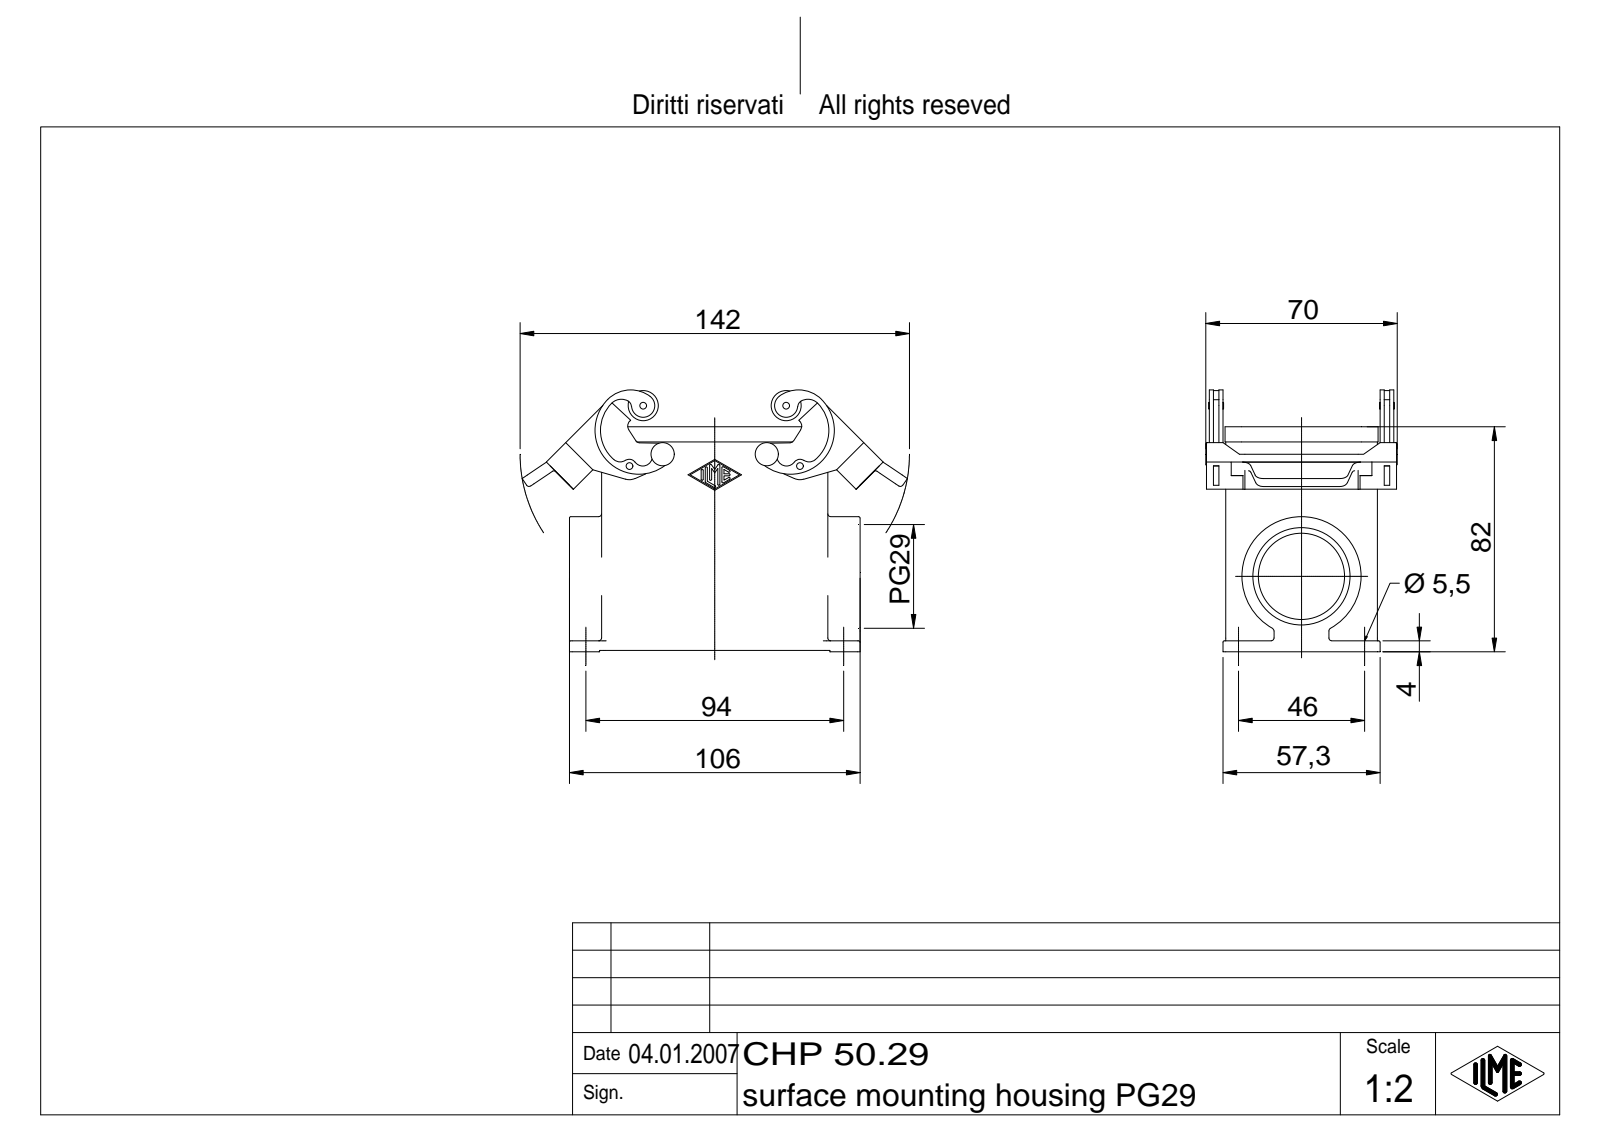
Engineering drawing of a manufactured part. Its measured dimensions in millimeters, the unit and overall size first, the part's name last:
Units: millimetres
Overall size (bounding box): 140.49 × 95.44 × 69.8
Round holes (diameter × count): ⌀2 ×4, ⌀2.46 ×4, ⌀3.1 ×4, ⌀2.5 ×2, ⌀5.5 ×2, ⌀31.48 ×1, ⌀35.48 ×1
Round bosses / shafts (diameter × count): ⌀11 ×2, ⌀5 ×2, ⌀3 ×2, ⌀43.5 ×1
Partial cylindrical surfaces — rounded edges, fillets, slot ends (radius × count): R1 ×30, R0.38 ×14, R0.5 ×14, R3 ×12, R6 ×8, R1.5 ×6, R2.5 ×6, R2 ×4
Main face-to-face distances: 3, 52.3, 55.3, 49.3, 3.5, 4, 11, 0.75, 79.5, 82.5
Hole centre spacings: 16, 22.56, 61.24, 66, 67.91, 14.32, 23.6, 30.41
Volume: 145 700 mm³ · Surface area: 76 731 mm²
Bodies: 1 solid, 911 faces (196 planar, 295 cylindrical, 420 other)
Part name (STEP PRODUCT): CHP 50.29
STEP written by: Autodesk Inventor 7 (AUTOMOTIVE_DESIGN)
